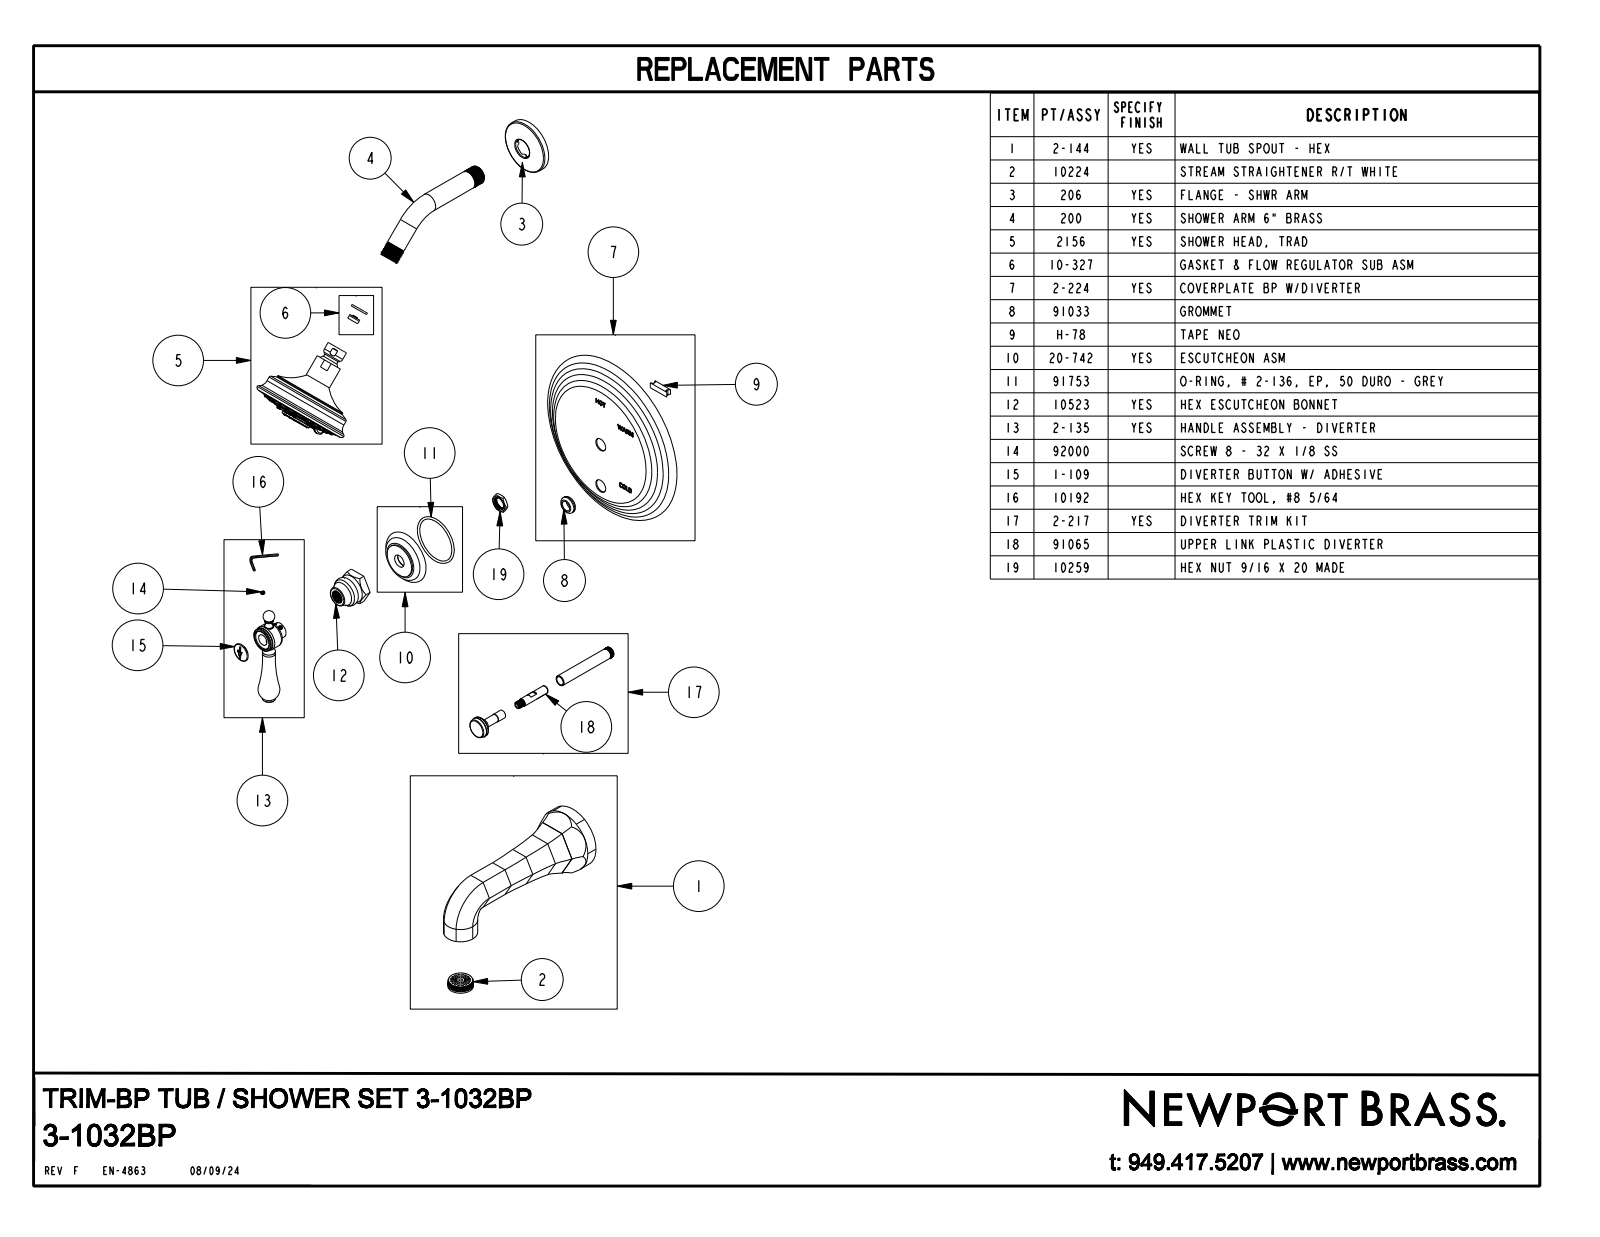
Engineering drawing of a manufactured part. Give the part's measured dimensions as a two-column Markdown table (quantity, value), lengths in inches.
| quantity | value |
| --- | --- |
| part name | 3-1032BP |
| STEP written by | CREO PARAMETRIC BY PTC INC, 2018400 (CONFIG_CONTROL_DESIGN) |
| units | inches |
| bodies | 3 solids, 1439 faces (283 planar, 241 cylindrical, 915 other) |
| overall size | 26.835 × 8.25 × 7.75 |
| volume | 71.4 in³ |
| surface area | 249.8 in² |
| round holes (diameter × count) | 0.059 × 8, 0.41 × 1, 0.855 × 1, 0.925 × 1 |
| round bosses / shafts (diameter × count) | 0.142 × 39, 0.165 × 23, 0.813 × 2, 3.81 × 1, 3.724 × 1, 3.24 × 1, 2.8 × 1, 2.38 × 1 |
| partial cylindrical surfaces (radius × count) | 0.079 × 8, 2.125 × 6, 0.015 × 2, 0.02 × 2, 1 × 2, 1.02 × 2, 0.02 × 1, 0.138 × 1 |
| main face-to-face distances | 0.754, 1.299, 0.995, 2.294, 0.063, 0.118, 0.181, 4.993, 3.694, 6.306 |
| hole center spacings | 0.443, 1.069, 0.819, 0.579, 0.578, 0.818, 1.157, 1.157 |
